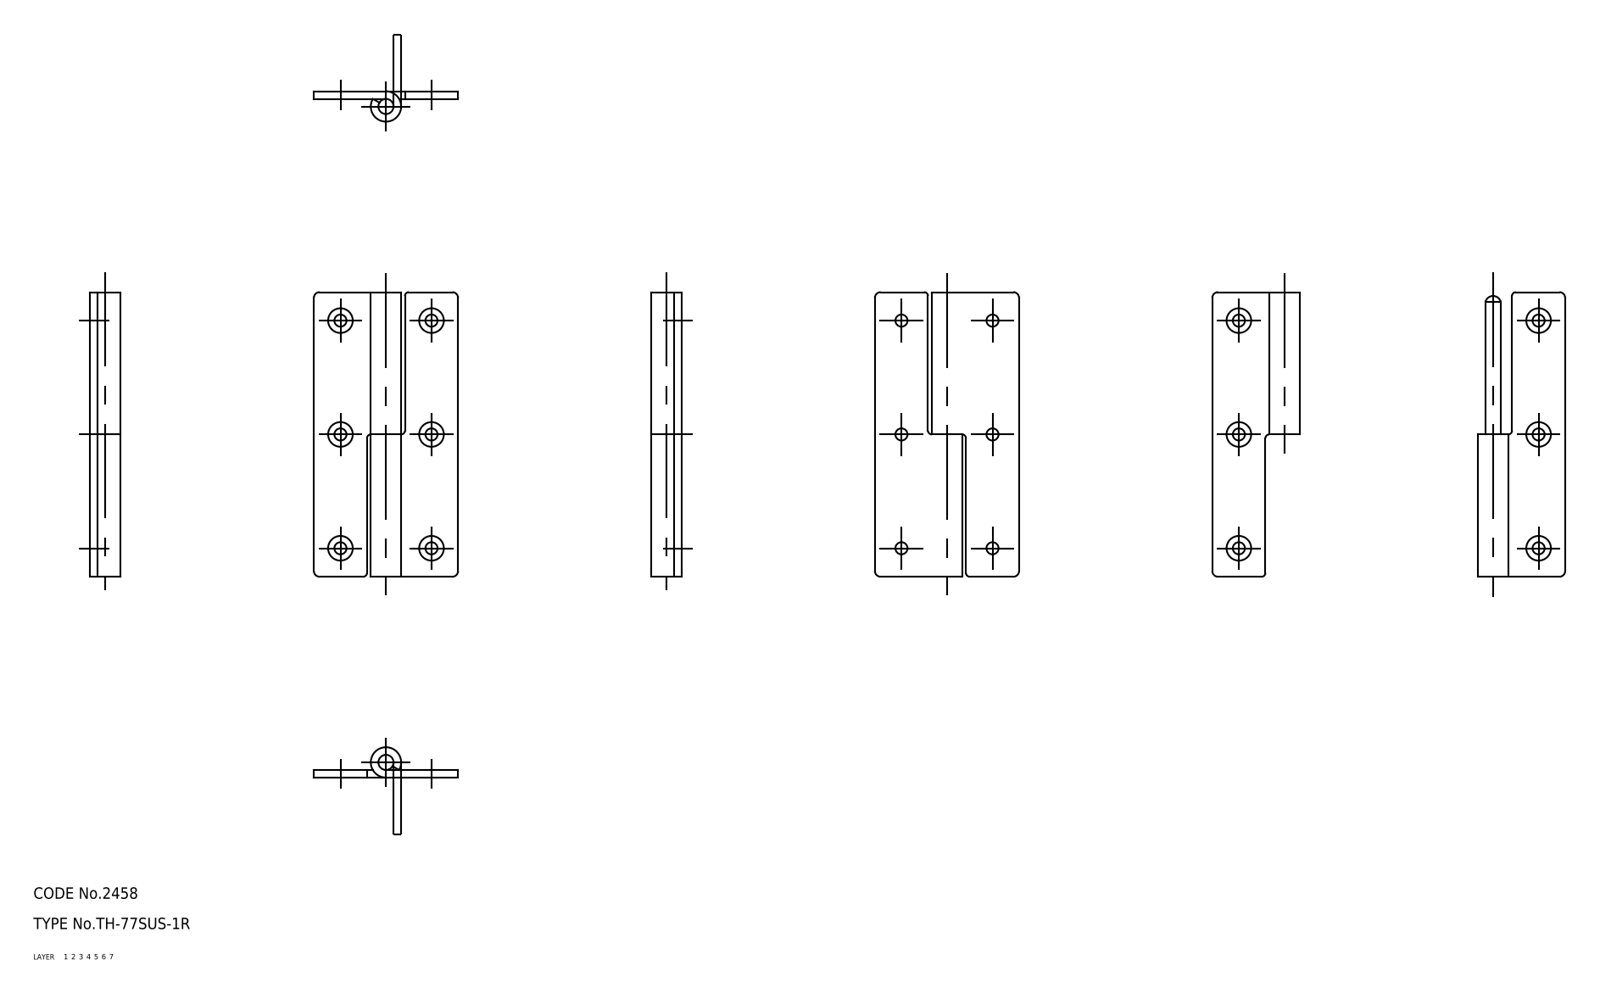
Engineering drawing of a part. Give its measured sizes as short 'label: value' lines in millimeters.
name: shaft; hinge piece_B; hinge piece_A; TH_77SUS_1R_16249_36
written by: CADfix (AUTOMOTIVE_DESIGN)
unit: mm
bodies: 3 solids, 56 faces (0 planar, 0 cylindrical, 56 other)
size: 75 × 38 × 8
volume: 8 013 mm³; area: 9 096 mm²
